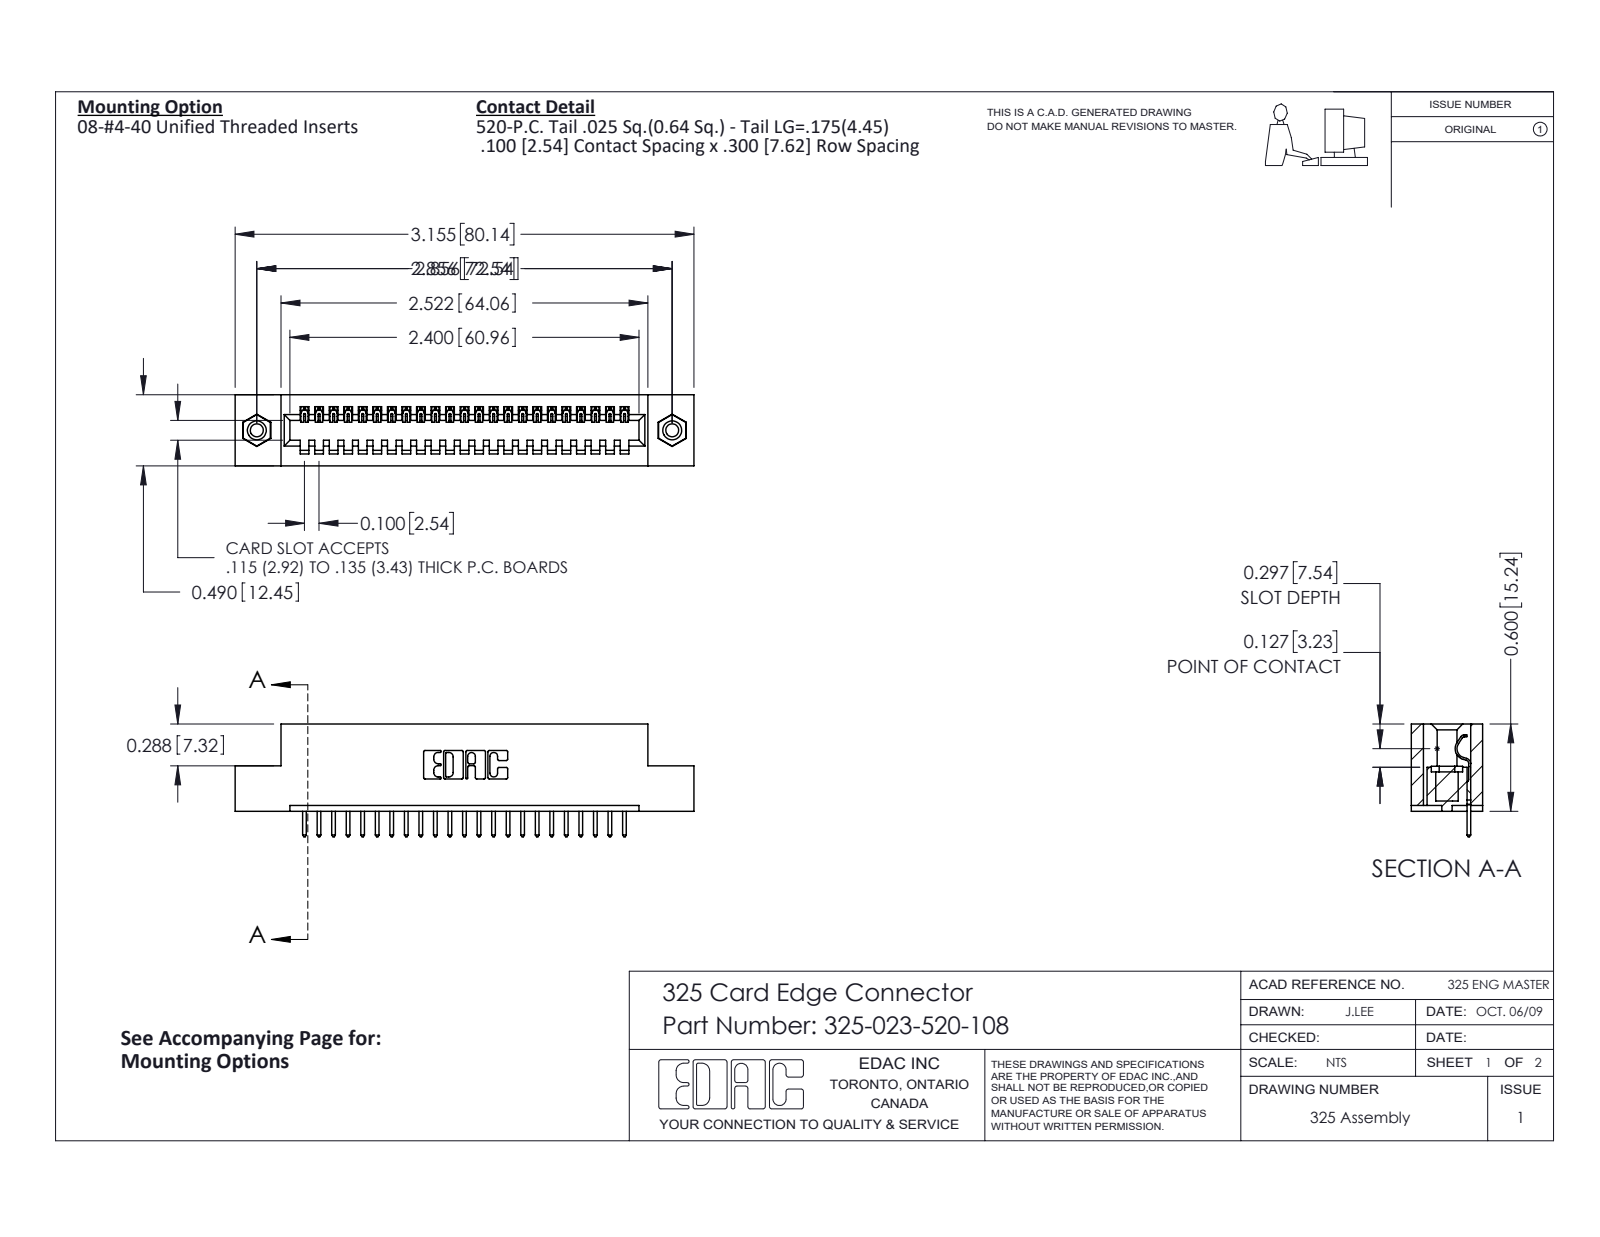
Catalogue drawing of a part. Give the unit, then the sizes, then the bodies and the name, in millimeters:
Units: millimetres
Overall size (bounding box): 80.1 × 19.7 × 12.4
Round holes (diameter × count): ⌀2.3 ×2, ⌀3.2 ×2, ⌀4.1 ×2
Round bosses / shafts (diameter × count): ⌀3.9 ×2
Partial cylindrical surfaces — rounded edges, fillets, slot ends (radius × count): R0.2 ×46, R0.3 ×46, R0.3 ×22, R0.2 ×6, R0.8 ×6, R0.7 ×3, R0.4 ×1, R0.6 ×1
Main face-to-face distances: 2.1, 10.3, 12.4, 7.6, 2.7, 9.7, 0.6, 1, 8.3, 15.2
Hole centre spacings: 72.5
Volume: 9 960 mm³ · Surface area: 10 330 mm²
Bodies: 26 solids, 1508 faces (1068 planar, 424 cylindrical, 16 other)
Part name (STEP PRODUCT): 325-292-001_325-293-120; 345-250-001_345-250-003-102; 325 Part_TI; 325-023-520-108
STEP written by: SolidWorks 2016 (CONFIG_CONTROL_DESIGN)
